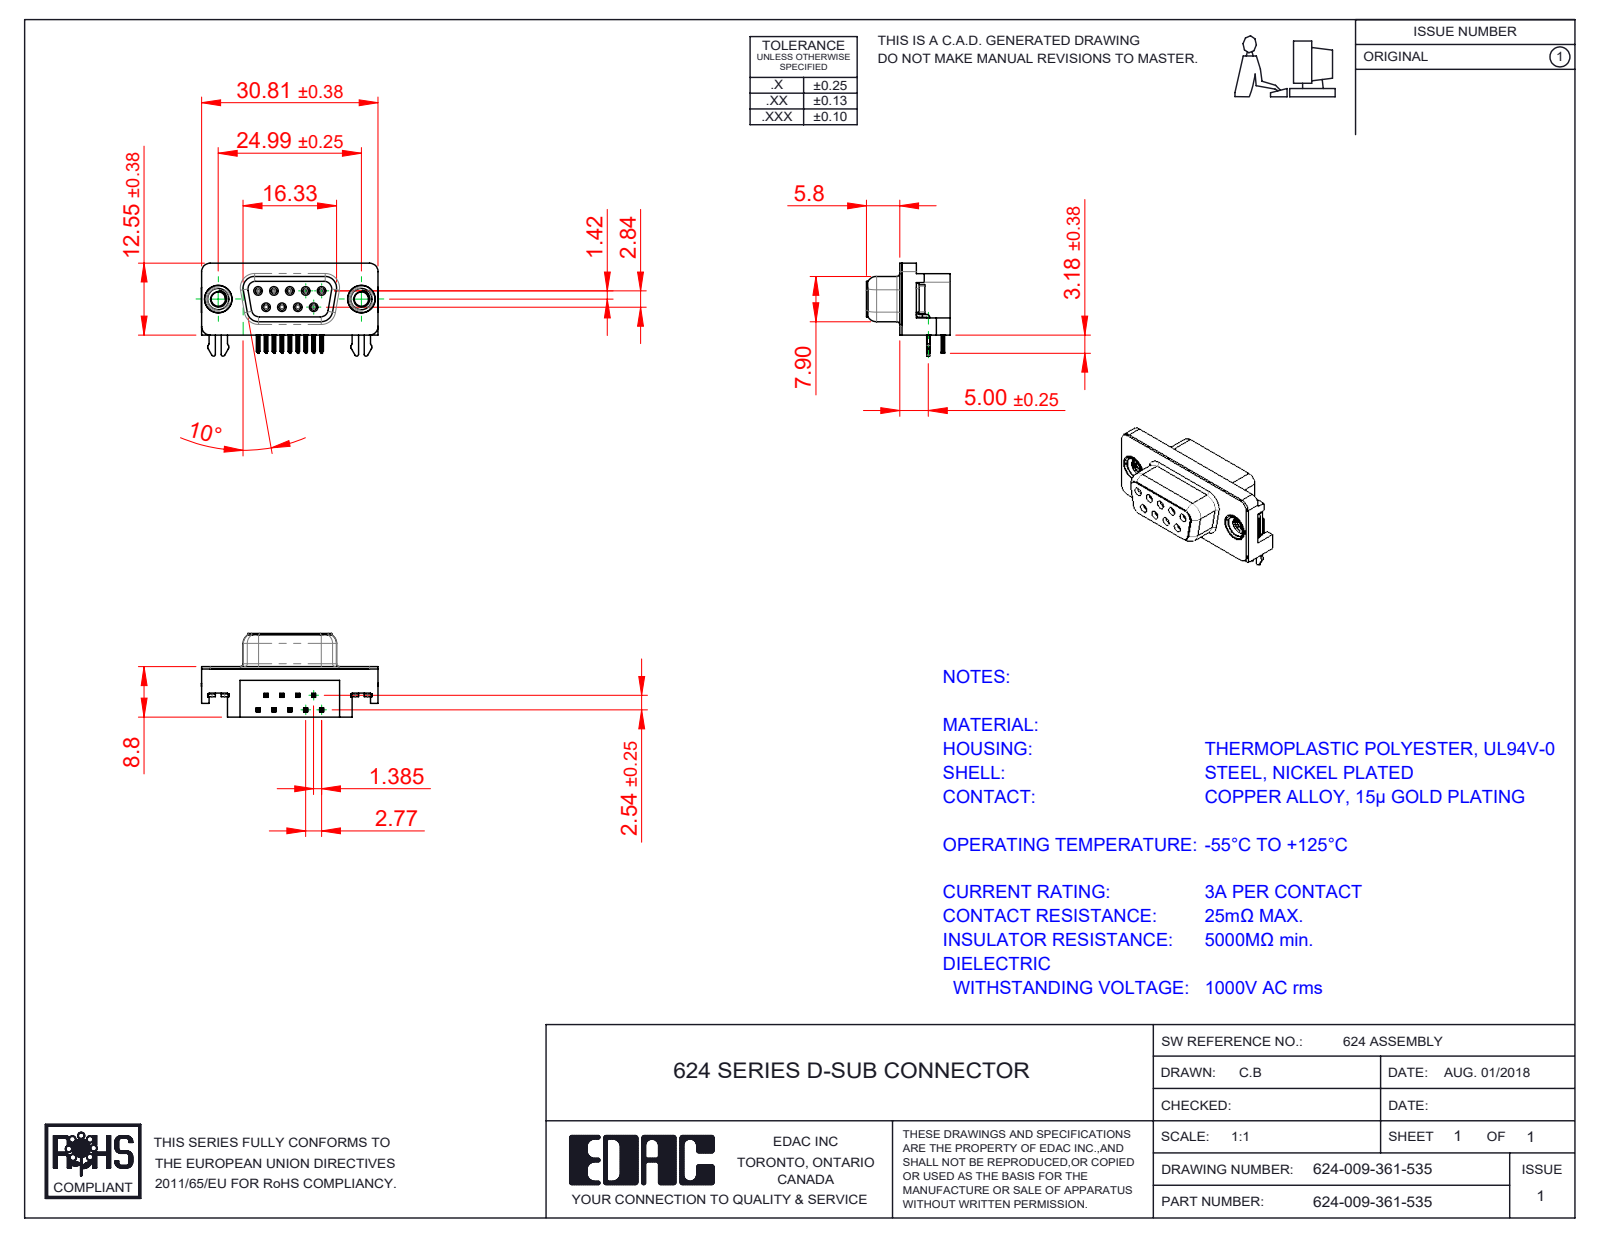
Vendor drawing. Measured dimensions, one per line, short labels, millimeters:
name: 624 Socket Bottom; 624 Housing_9 Socket; 624 Shell_9 Socket; 624 Contact Top (+3 more)
written by: SolidWorks 2016 (CONFIG_CONTROL_DESIGN)
unit: mm
bodies: 15 solids, 1552 faces (670 planar, 414 cylindrical, 468 other)
size: 30.89 × 16.25 × 14.6
volume: 2 941 mm³; area: 4 400 mm²
holes: 9× ⌀0.8, 9× ⌀0.9, 2× ⌀2.5, 2× ⌀4, 2× ⌀4.8, 2× ⌀5
bosses: 9× ⌀1.2, 2× ⌀4.9, 2× ⌀4.75, 2× ⌀3.9
rounds: 72× R0.1, 36× R0.15, 18× R0.35, 10× R0.5, 10× R1, 9× R0.34, 8× R0.25, 8× R1.35
face distances: 0.4, 8.4, 8.8, 2.9, 2.5, 6.2, 5.9, 0.35, 0.85, 10.69
hole spacings: 3.16, 2.77, 5.54, 5.03, 5.04, 8.31, 7.48, 7.49
